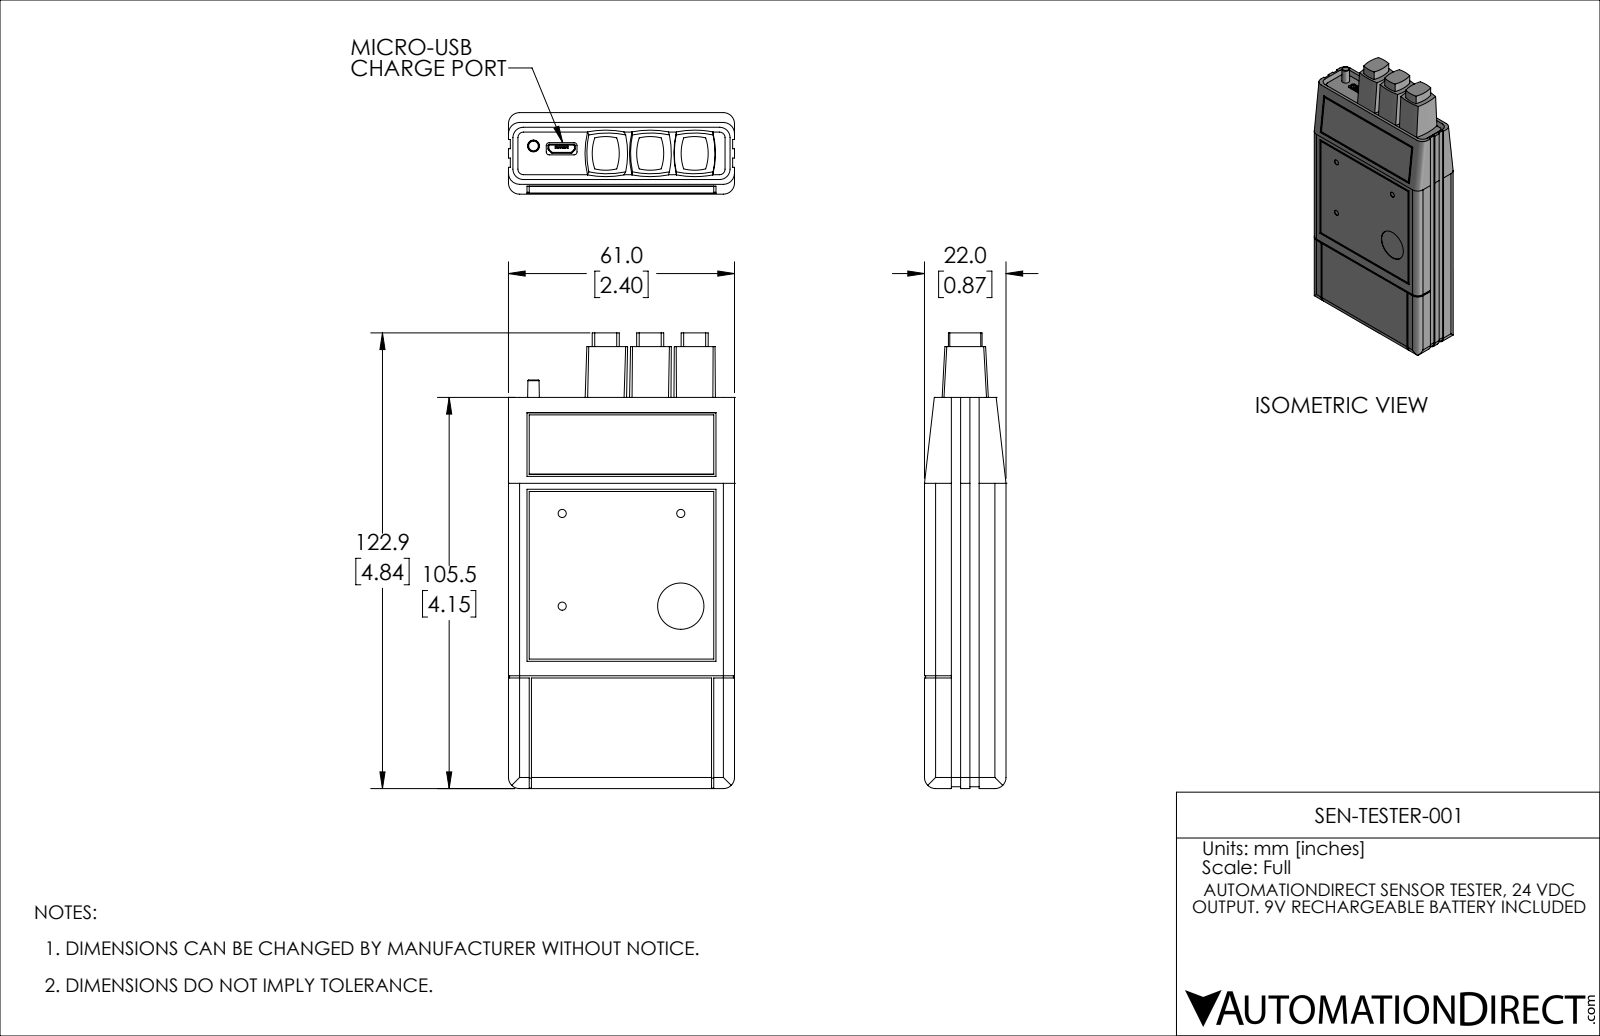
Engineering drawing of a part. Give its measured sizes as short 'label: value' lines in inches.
name: SEN-TESTER-001
written by: SolidWorks 2021 (AUTOMOTIVE_DESIGN)
unit: in
bodies: 1 solid, 196 faces (123 planar, 56 cylindrical, 17 other)
size: 4.839 × 2.402 × 0.866
volume: 8.584 in³; area: 35.23 in²
holes: 3× ⌀0.087, 1× ⌀0.492
rounds: 8× R0.118, 6× R0.489, 6× R0.519, 4× R0.006, 4× R0.016, 4× R0.031, 3× R0.106, 2× R0.012
face distances: 0.866, 0.02, 2.382, 2.402, 2.362, 0.098, 0.197, 0.285, 0.384, 0.482
hole spacings: 0.984, 1.26, 1.599
